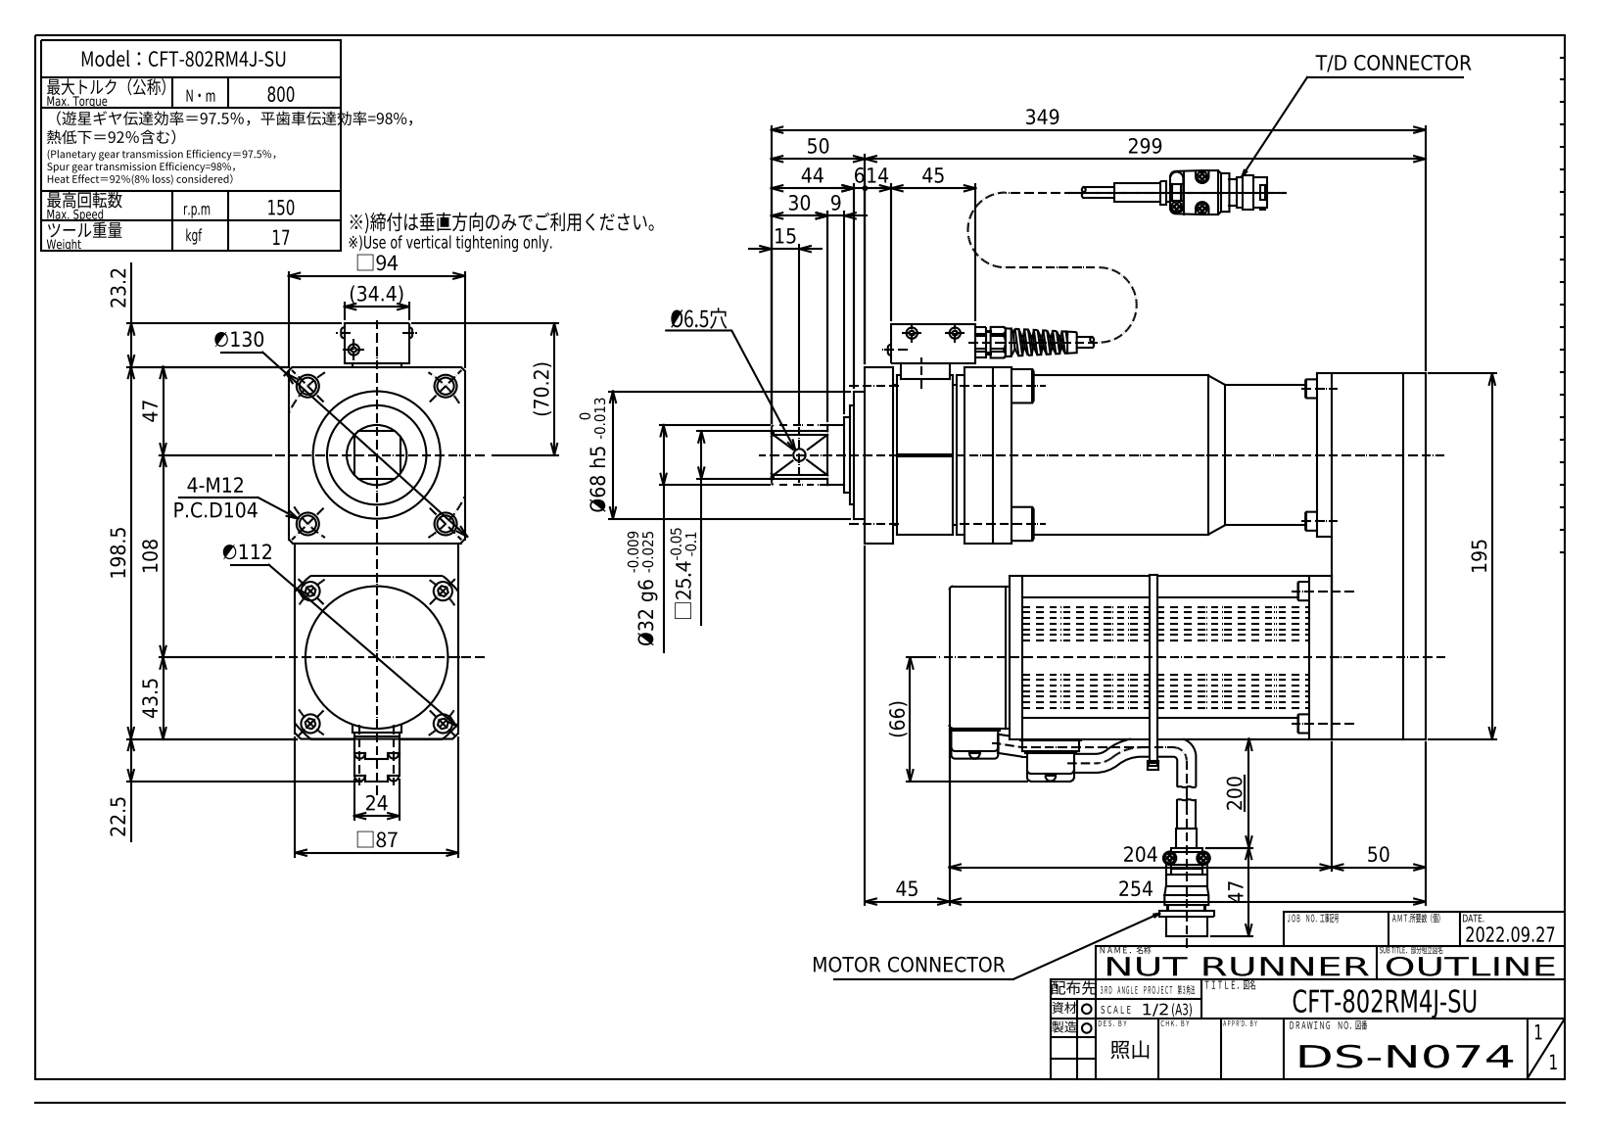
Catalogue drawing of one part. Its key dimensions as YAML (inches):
part_name: "CFT-802RM4J-SU(DS-N074)_OUTLINE_20220929"
step_written_by: "Autodesk Inventor 2021 (AUTOMOTIVE_DESIGN)"
units: inches
bodies: {solids: 13, faces: 1172, planar: 714, cylindrical: 315, other: 143}
overall_size: [13.74, 9.614, 3.701]
volume: 223.4
surface_area: 516.4
round_holes:
  - {diameter: 0.197, count: 6}
  - {diameter: 0.26, count: 6}
  - {diameter: 0.433, count: 6}
  - {diameter: 0.256, count: 5}
  - {diameter: 0.098, count: 4}
  - {diameter: 0.157, count: 4}
  - {diameter: 0.404, count: 4}
  - {diameter: 0.097, count: 3}
  - {diameter: 0.311, count: 2}
  - {diameter: 0.315, count: 2}
  - {diameter: 0.138, count: 1}
  - {diameter: 0.354, count: 1}
round_bosses_or_shafts:
  - {diameter: 0.394, count: 8}
  - {diameter: 0.315, count: 7}
  - {diameter: 0.224, count: 7}
  - {diameter: 0.276, count: 5}
  - {diameter: 0.709, count: 4}
  - {diameter: 0.335, count: 4}
  - {diameter: 0.295, count: 4}
  - {diameter: 0.118, count: 3}
partial_cylinders:
  - {radius: 0.024, count: 48}
  - {radius: 0.039, count: 28}
  - {radius: 0.02, count: 13}
  - {radius: 0.118, count: 8}
  - {radius: 0.059, count: 7}
  - {radius: 0.197, count: 6}
  - {radius: 0.012, count: 4}
  - {radius: 0.079, count: 4}
face_to_face_distances: [0.118, 0.059, 0.236, 3.425, 0.177, 1.772, 0.591, 0.354, 1.89, 2.008]
hole_center_spacings: [2.047, 2.895, 2.953, 3.781, 2.362, 0.336, 0.676, 0.729]
